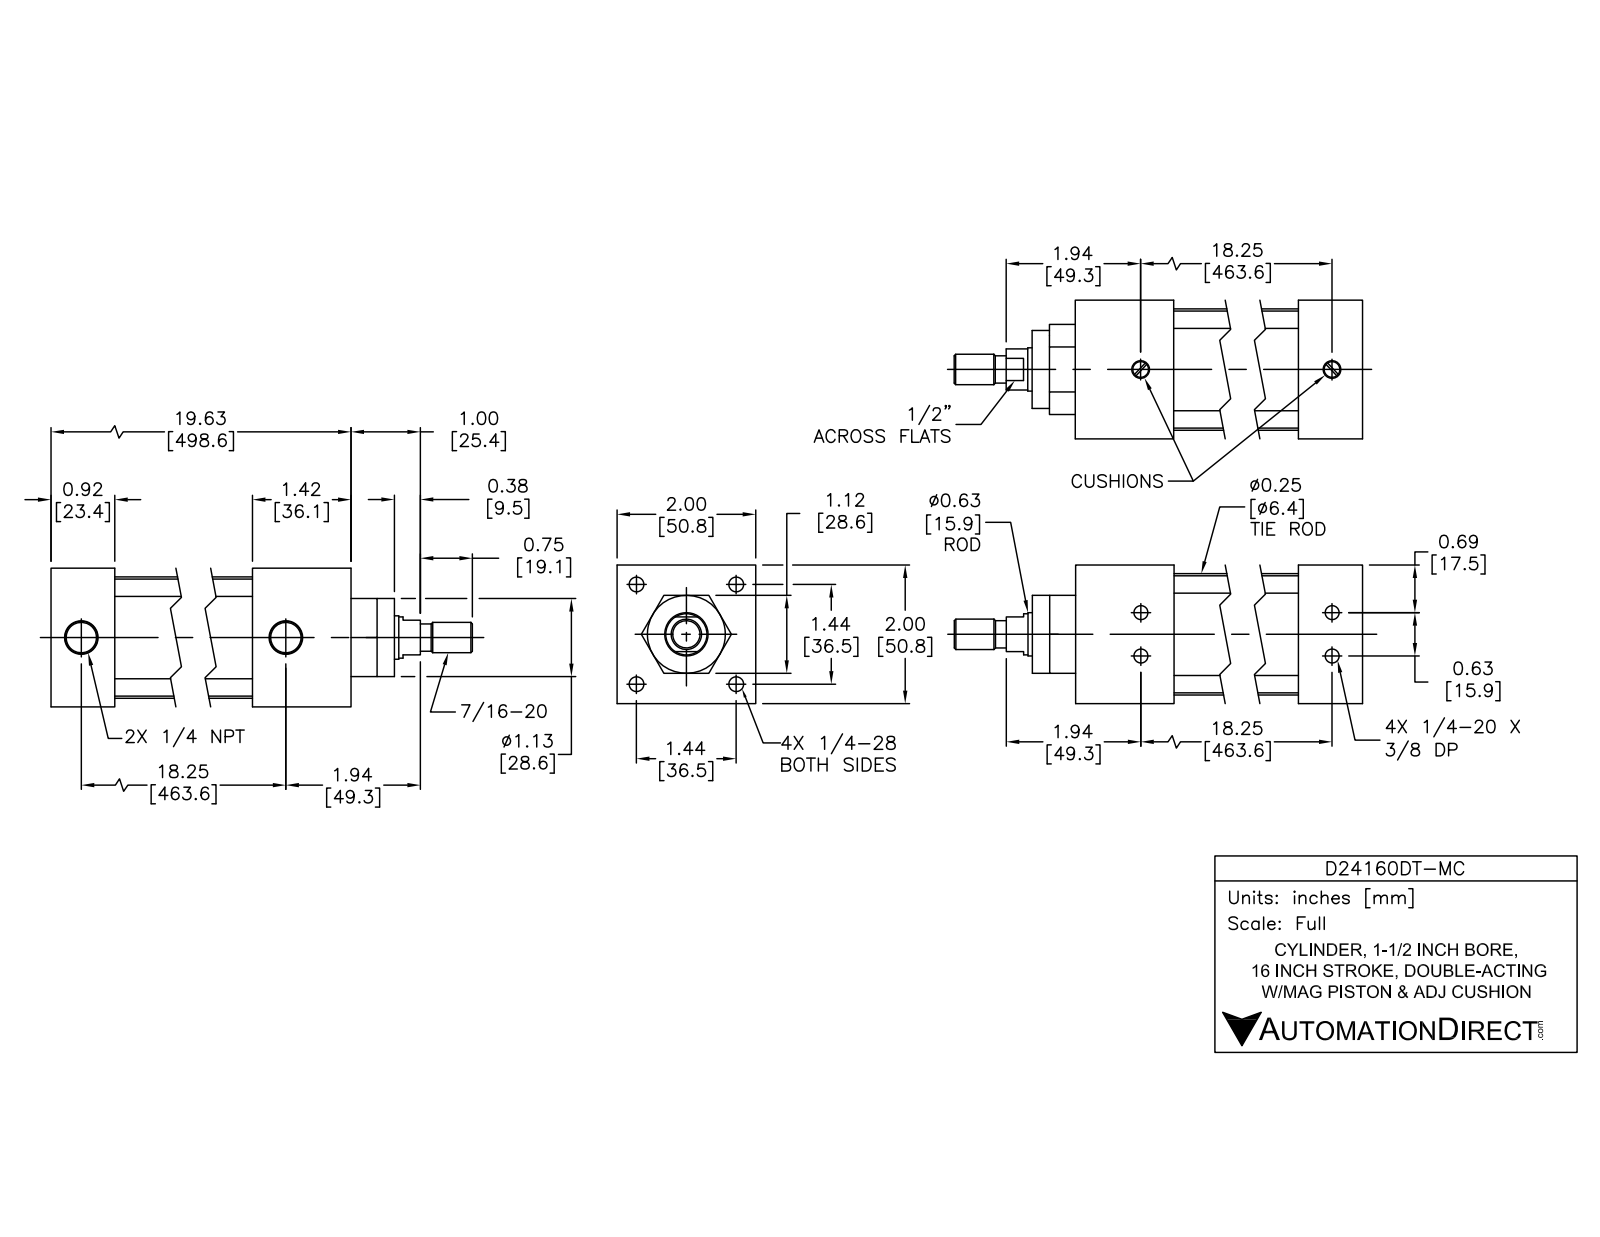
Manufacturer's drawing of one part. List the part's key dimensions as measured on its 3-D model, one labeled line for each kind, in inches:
Part name (STEP PRODUCT): D24160DT-MC; D24160DT-M PISTON; D24160DT-M BODY
STEP written by: SolidWorks 2015 (AUTOMOTIVE_DESIGN)
Units: inches
Bodies: 12 solids, 303 faces (99 planar, 114 cylindrical, 90 other)
Overall size (bounding box): 21.371 × 2 × 2
Volume: 30.24 in³ · Surface area: 332.3 in²
Round holes (diameter × count): ⌀0.196 ×4, ⌀0.211 ×4, ⌀0.281 ×4, ⌀0.406 ×4, ⌀0.297 ×2, ⌀0.477 ×2, ⌀0.625 ×1, ⌀0.628 ×1, ⌀1.5 ×1
Round bosses / shafts (diameter × count): ⌀0.39 ×4, ⌀0.25 ×4, ⌀0.222 ×4, ⌀1.75 ×1, ⌀1.497 ×1, ⌀1.121 ×1, ⌀0.622 ×1, ⌀0.59 ×1
Partial cylindrical surfaces — rounded edges, fillets, slot ends (radius × count): R0.2 ×4
Main face-to-face distances: 2, 0.08, 17.201, 19.621, 1.42, 18.201, 18.701, 17.281, 0.92, 18.601
Hole centre spacings: 1.434, 18.249, 0.312, 0.313, 0.625, 1.014, 2.028, 18.247
